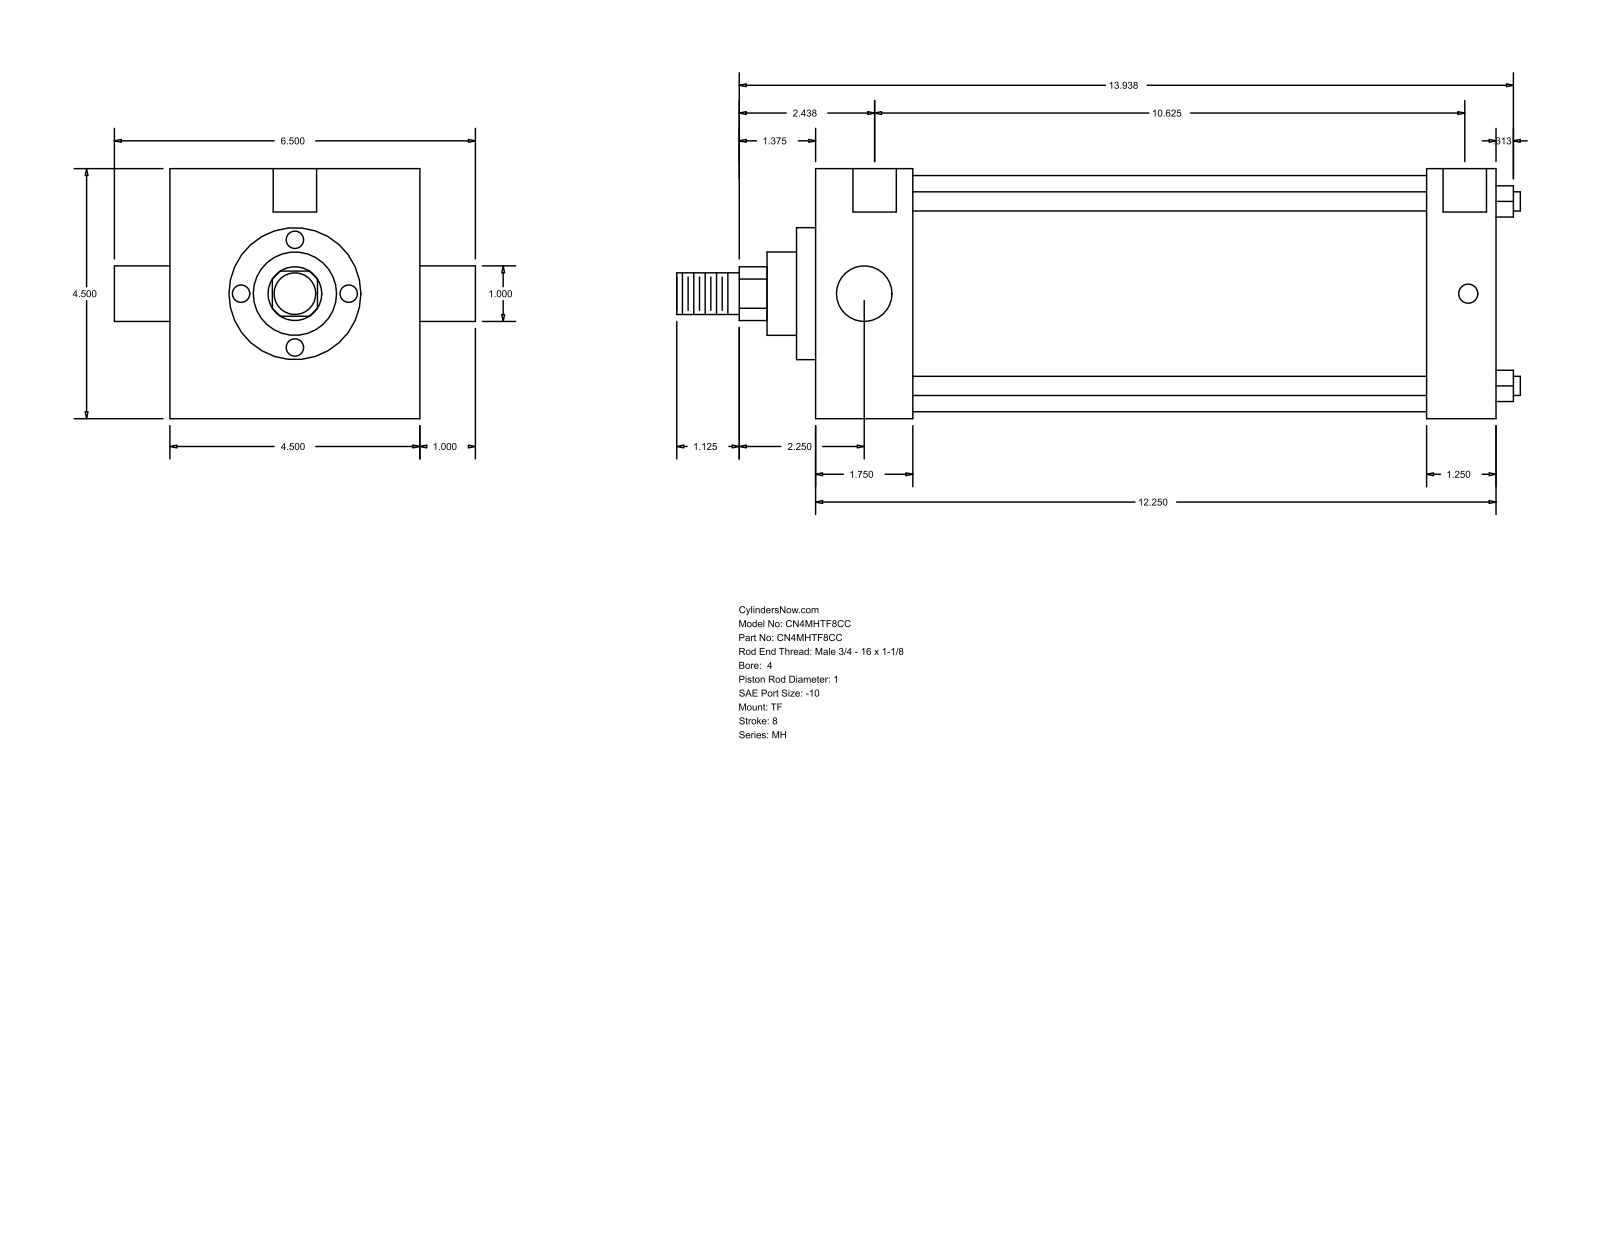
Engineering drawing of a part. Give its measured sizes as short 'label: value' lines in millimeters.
name: MH_TF__0400_1
written by: GSSL Pune (CONFIG_CONTROL_DESIGN)
unit: mm
bodies: 0 solids, 86 faces (61 planar, 25 cylindrical, 0 other)
size: 385.76 × 165.1 × 114.3
holes: 3× ⌀8.73, 2× ⌀19.84
bosses: 4× ⌀8.76, 2× ⌀25.4, 1× ⌀107.95, 1× ⌀60.33, 1× ⌀38.1, 1× ⌀19.05
rounds: 1× R12.29
face distances: 114.3, 311.15, 44.46, 266.69, 279.4, 234.94, 31.75, 8.73, 53.19, 288.13
hole spacings: 1.58, 1.59, 269.88, 271.46, 271.47, 273.05
